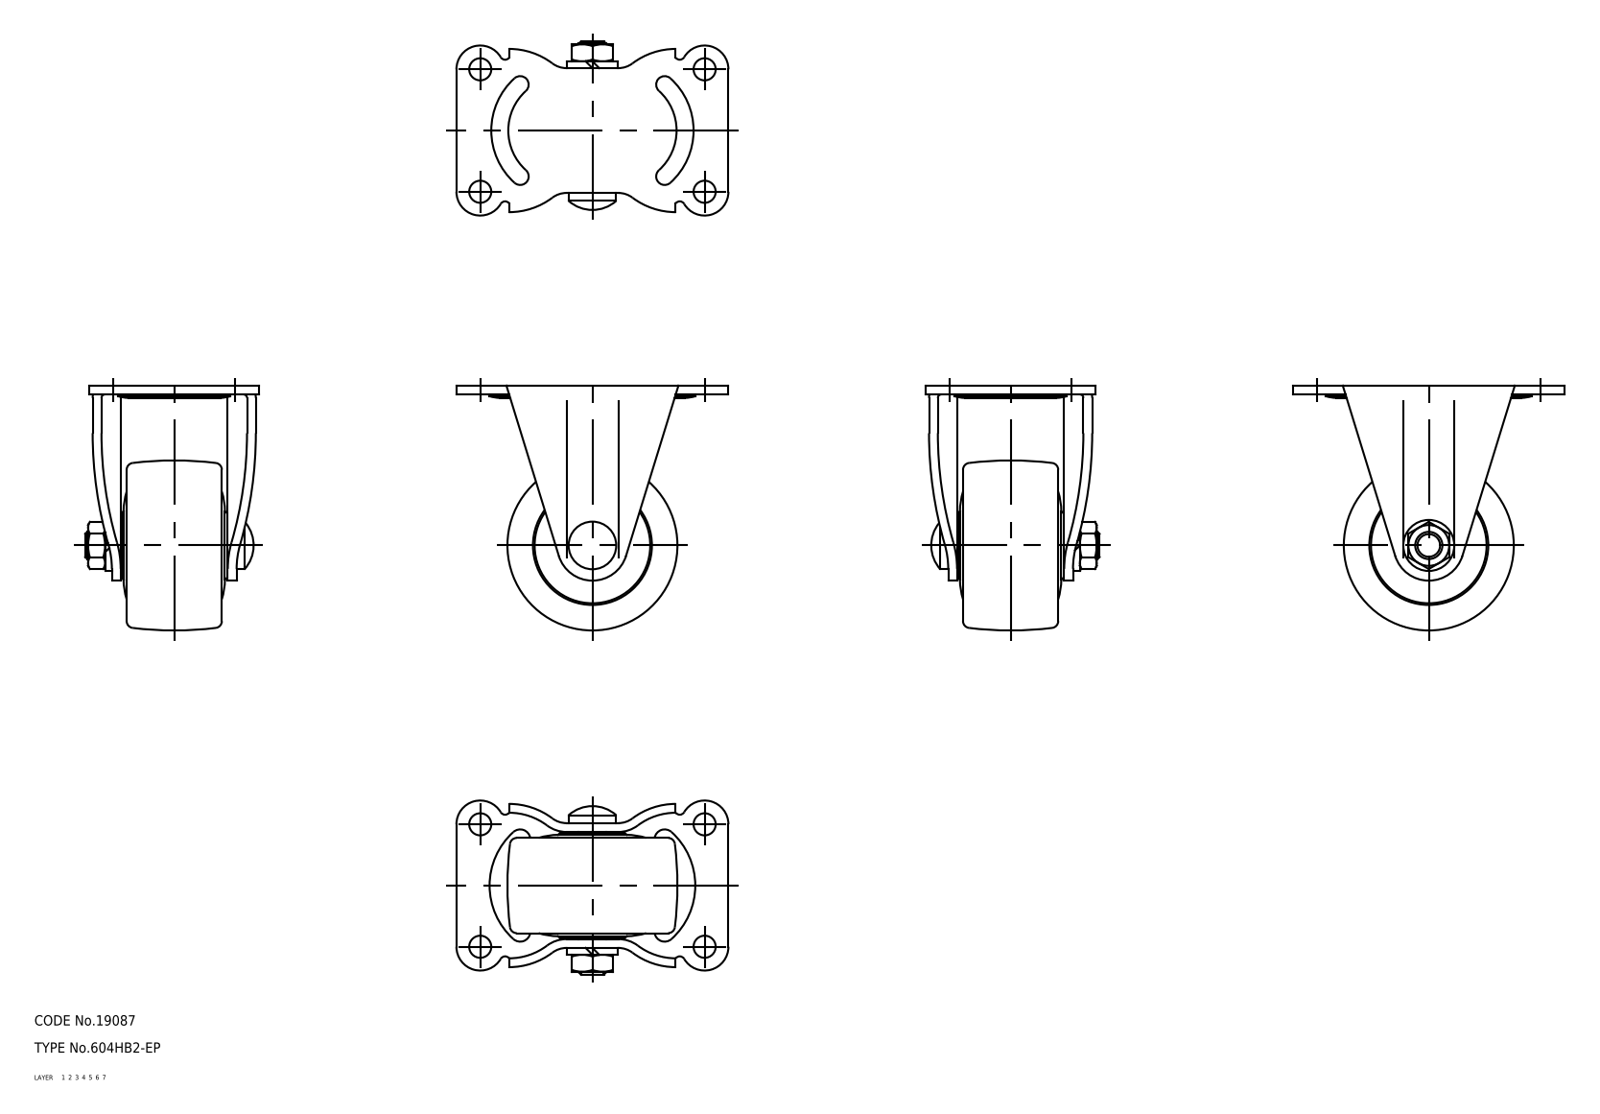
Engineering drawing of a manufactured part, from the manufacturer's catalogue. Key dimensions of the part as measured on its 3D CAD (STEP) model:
Part name (STEP PRODUCT): wheel; axle; No_604HB2_EP_14564_36
STEP written by: CADfix (AUTOMOTIVE_DESIGN)
Units: millimetres
Bodies: 3 solids, 164 faces (0 planar, 0 cylindrical, 164 other)
Overall size (bounding box): 80 × 72 × 51.15
Volume: 73 962 mm³ · Surface area: 26 913 mm²
